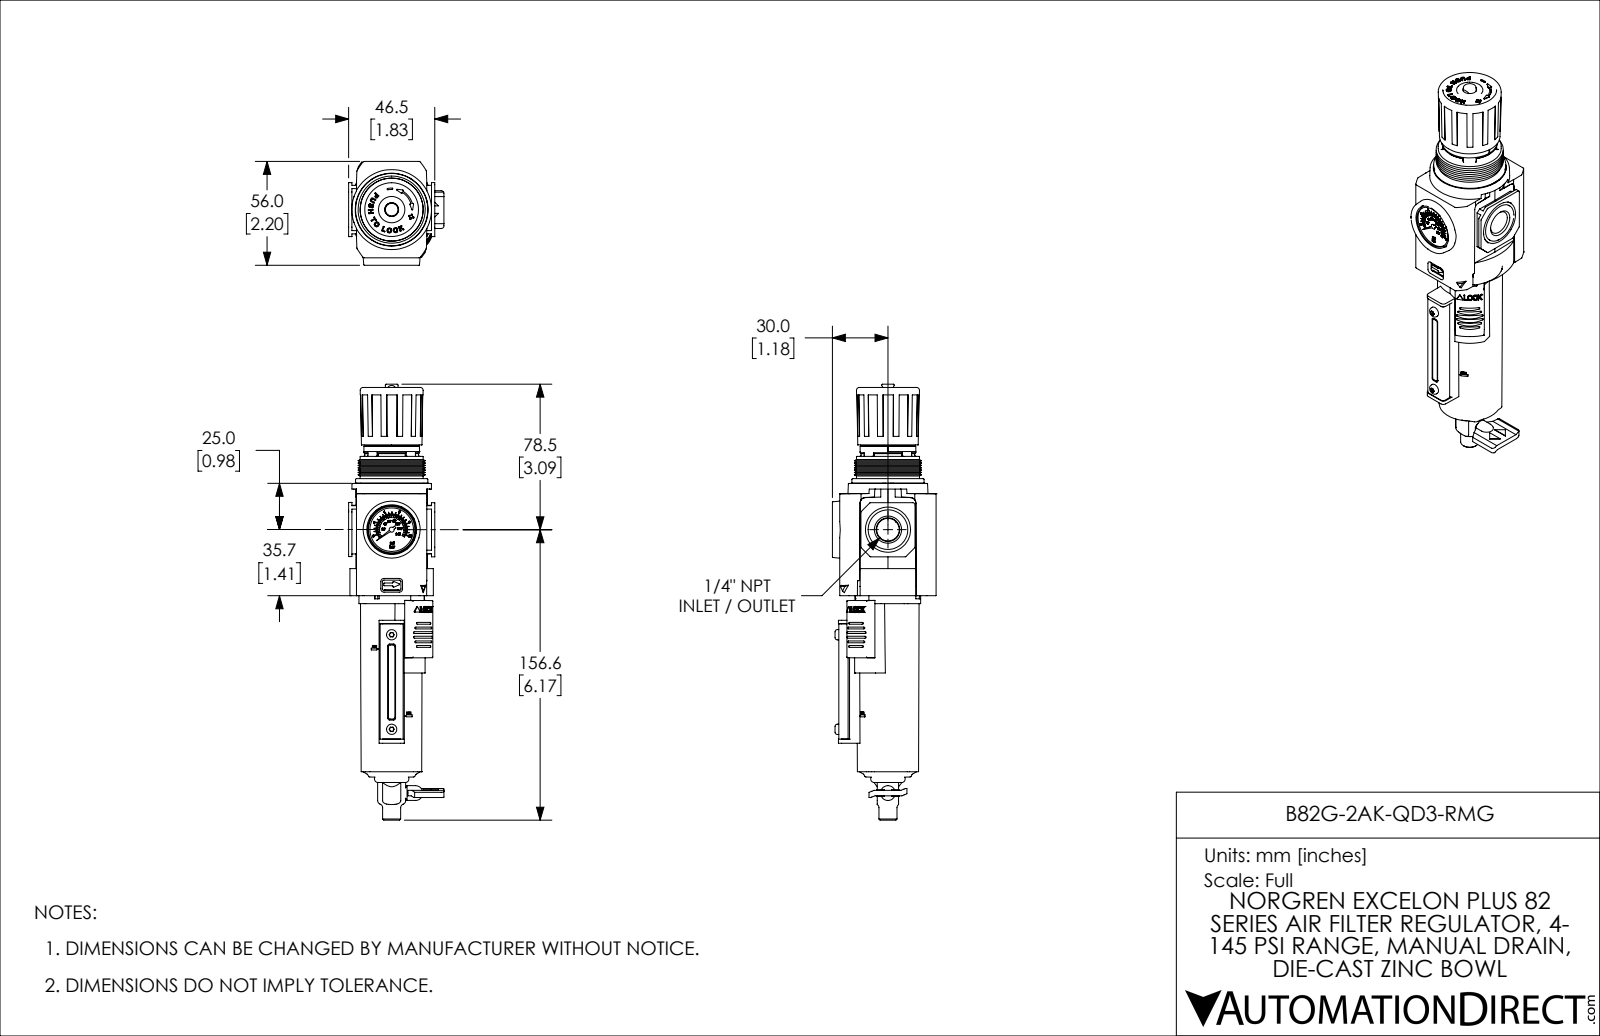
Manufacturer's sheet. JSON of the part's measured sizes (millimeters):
{"part_name": "B82G-2AK-QD3-RMG", "step_written_by": "SolidWorks 2021 (CONFIG_CONTROL_DESIGN)", "units": "millimeters", "bodies": {"solids": 8, "faces": 2663, "planar": 1028, "cylindrical": 1243, "other": 392}, "overall_size": [235.1, 56, 51.5], "volume_mm3": 280200, "surface_area_mm2": 75350, "round_holes": [[2.5, 4], [3.5, 2], [3.3, 1], [5, 1], [6, 1], [6.4, 1], [16, 1], [23.5, 1], [28, 1], [34.4, 1]], "round_bosses_or_shafts": [[5.7, 2], [5.5, 2], [3, 2], [39, 1], [35.3, 1], [34.4, 1], [34, 1], [32.8, 1]], "partial_cylinders_radius": [[0.5, 50], [1, 38], [0.2, 25], [0.8, 20], [0.2, 19], [0.3, 13], [0.3, 12], [0.3, 12]], "face_to_face_distances": [1.5, 50.5, 43, 9, 41.5, 7.5, 36, 37.5, 6, 4.6], "hole_center_spacings": [16, 27.7, 32, 68.7, 84.5, 75.3]}
